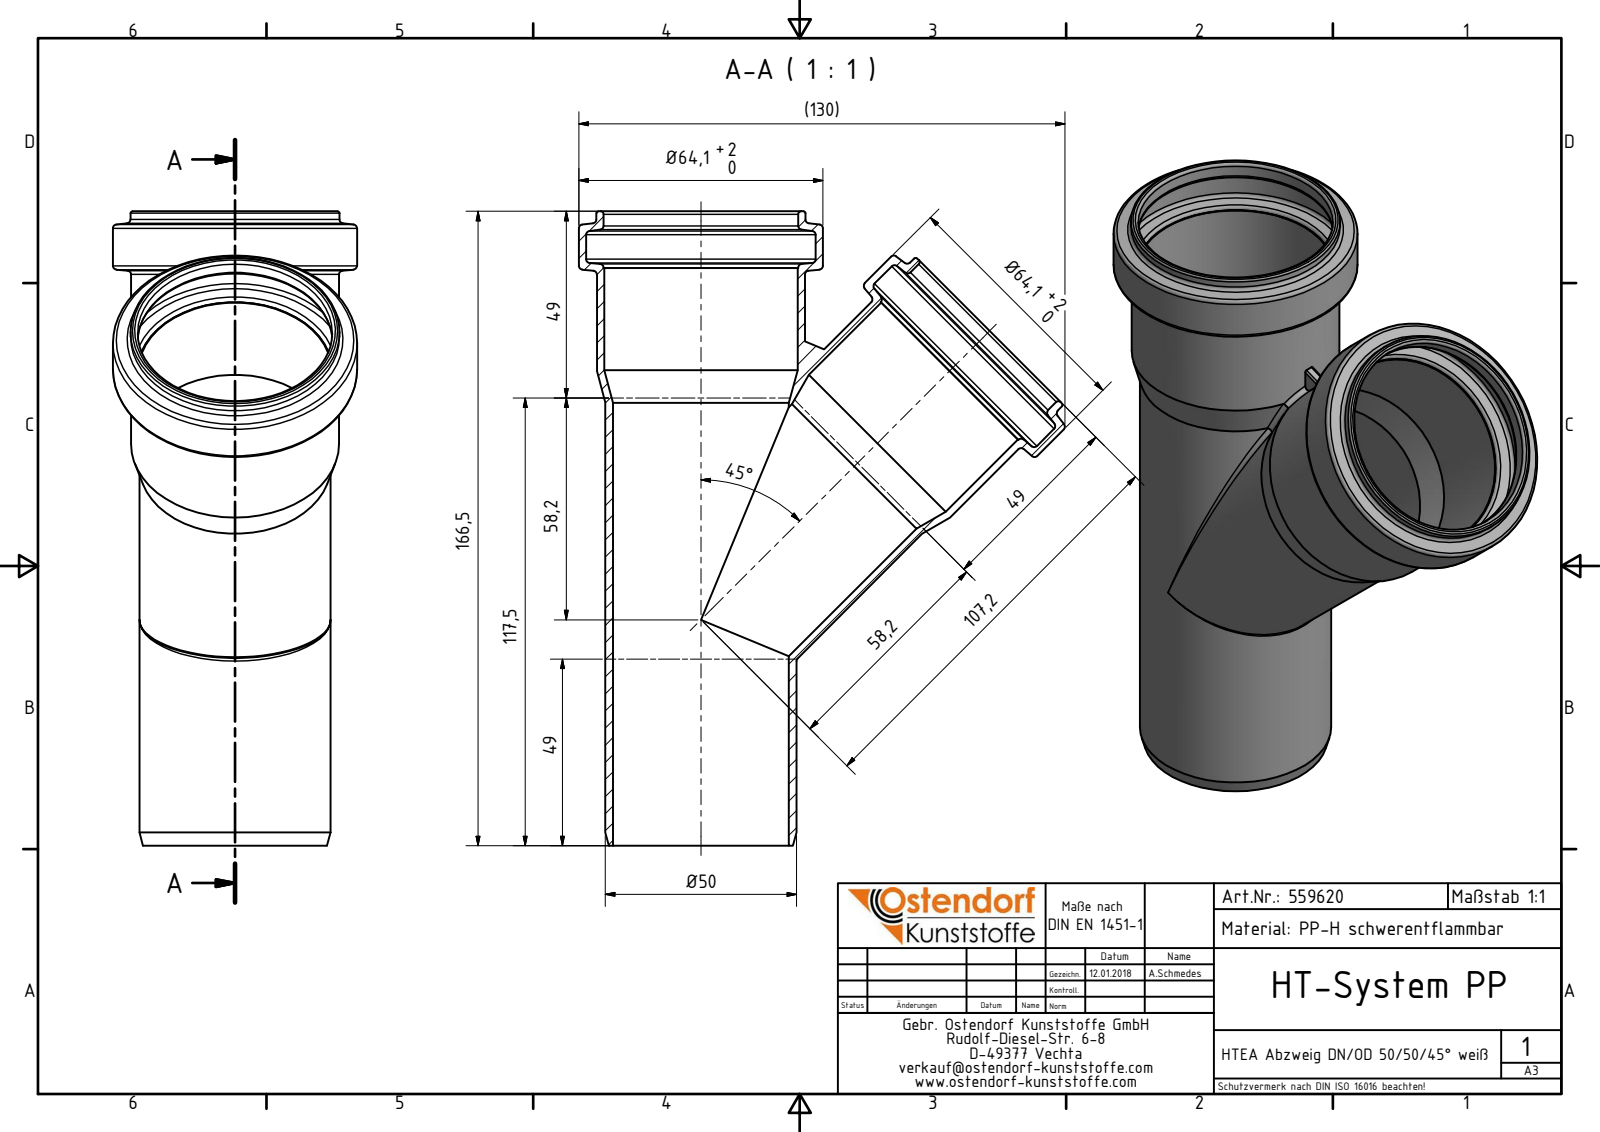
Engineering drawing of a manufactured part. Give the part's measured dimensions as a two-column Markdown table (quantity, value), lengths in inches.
| quantity | value |
| --- | --- |
| part name | 559620 HTEA DN_OD 50_50_45° weiß |
| STEP written by | Autodesk Inventor 2016 (AUTOMOTIVE_DESIGN) |
| units | inches |
| bodies | 1 solid, 68 faces (8 planar, 20 cylindrical, 40 other) |
| overall size | 6.555 × 5.025 × 2.524 |
| volume | 4.729 in³ |
| surface area | 122.8 in² |
| round holes (diameter × count) | 2.012 × 3, 1.819 × 2, 2 × 2, 2.374 × 2 |
| round bosses / shafts (diameter × count) | 2.524 × 2, 2.161 × 2, 2.15 × 2, 1.976 × 2 |
| partial cylindrical surfaces (radius × count) | 0.02 × 2 |
| main face-to-face distances | 6.555, 5.969, 0.587, 0.586, 0.11 |
